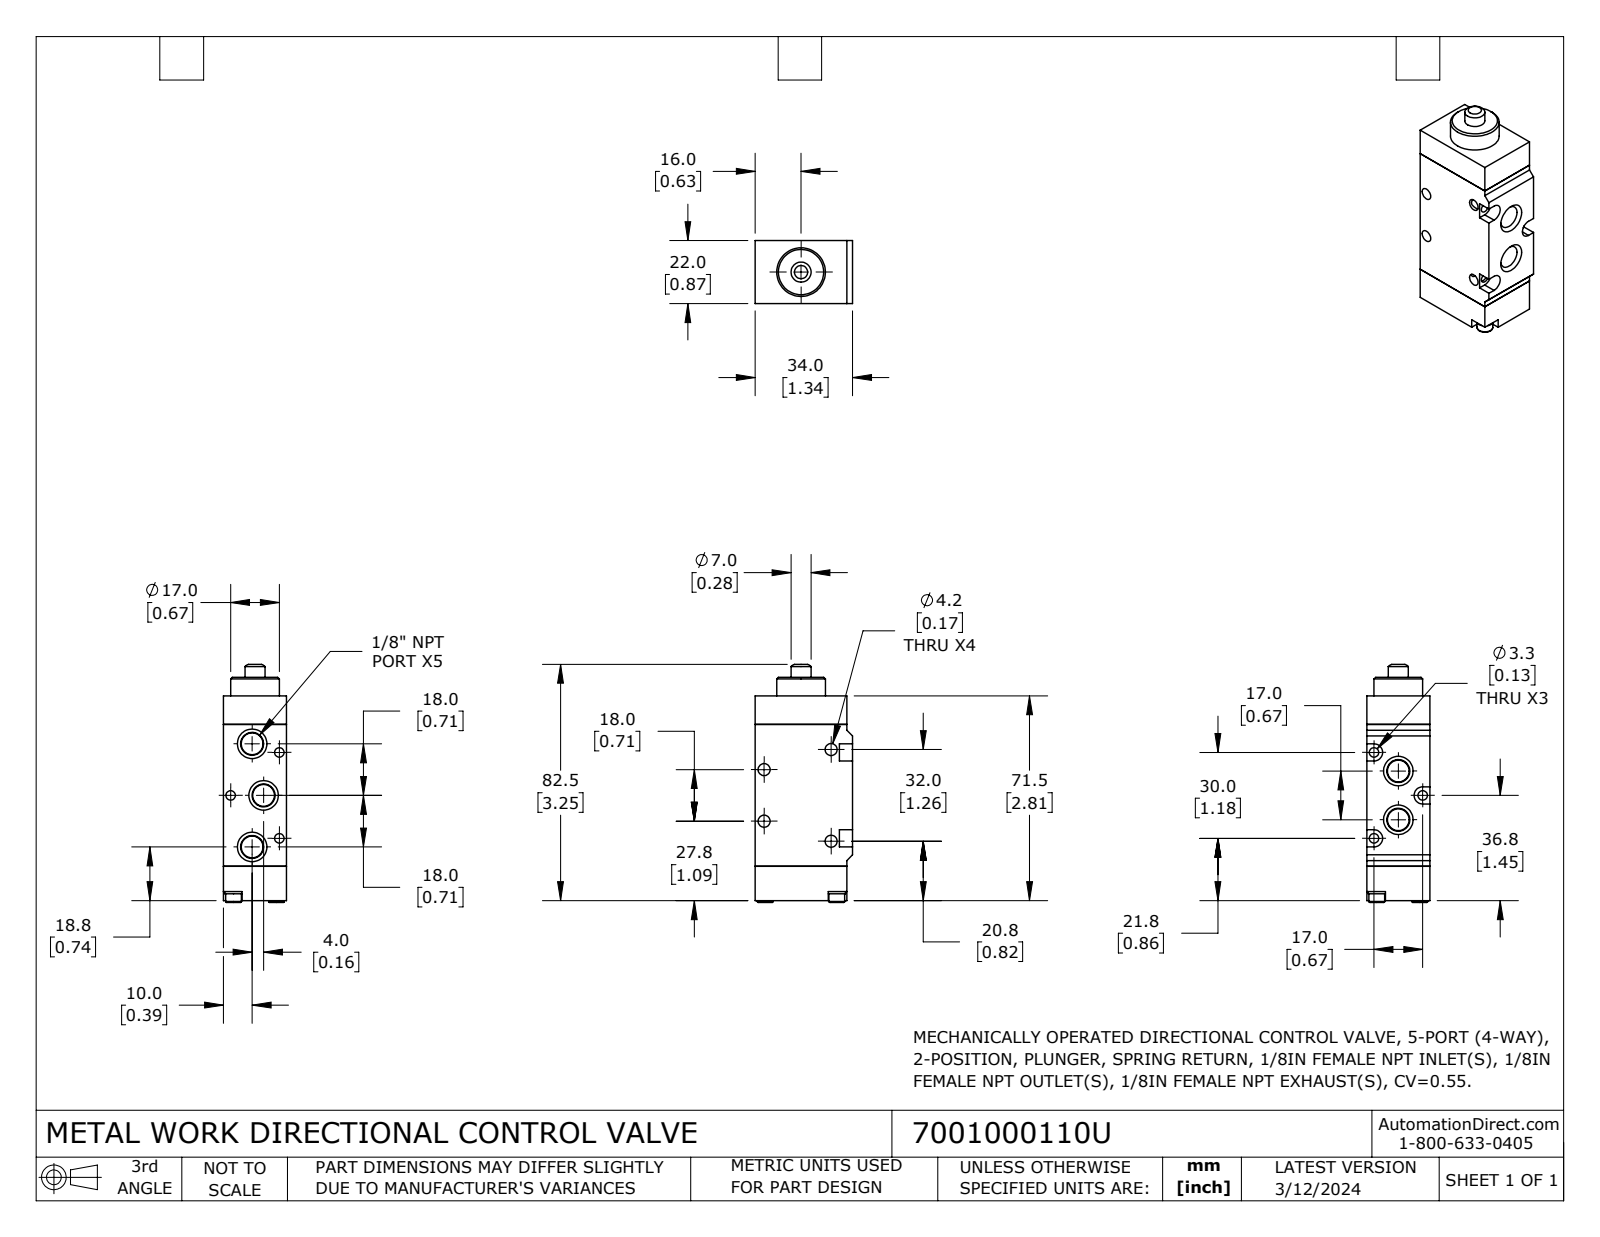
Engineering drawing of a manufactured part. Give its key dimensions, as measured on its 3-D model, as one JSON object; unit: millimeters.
{"part_name": "7001000110U", "step_written_by": "SolidWorks 2023 (CONFIG_CONTROL_DESIGN)", "units": "millimeters", "bodies": {"solids": 7, "faces": 173, "planar": 78, "cylindrical": 43, "other": 52}, "overall_size": [83.1, 34, 22], "volume_mm3": 49670, "surface_area_mm2": 15920, "round_holes": [[4.2, 4], [3.3, 3], [3, 2]], "round_bosses_or_shafts": [[6, 2], [5.5, 2], [17, 1], [7, 1]], "partial_cylinders_radius": [[3, 3]], "face_to_face_distances": [22, 49.5, 34, 12, 61.5, 2, 32, 71.5, 59.5, 10], "hole_center_spacings": [22.7, 24.4, 34.2, 18, 29.2, 30, 32]}
